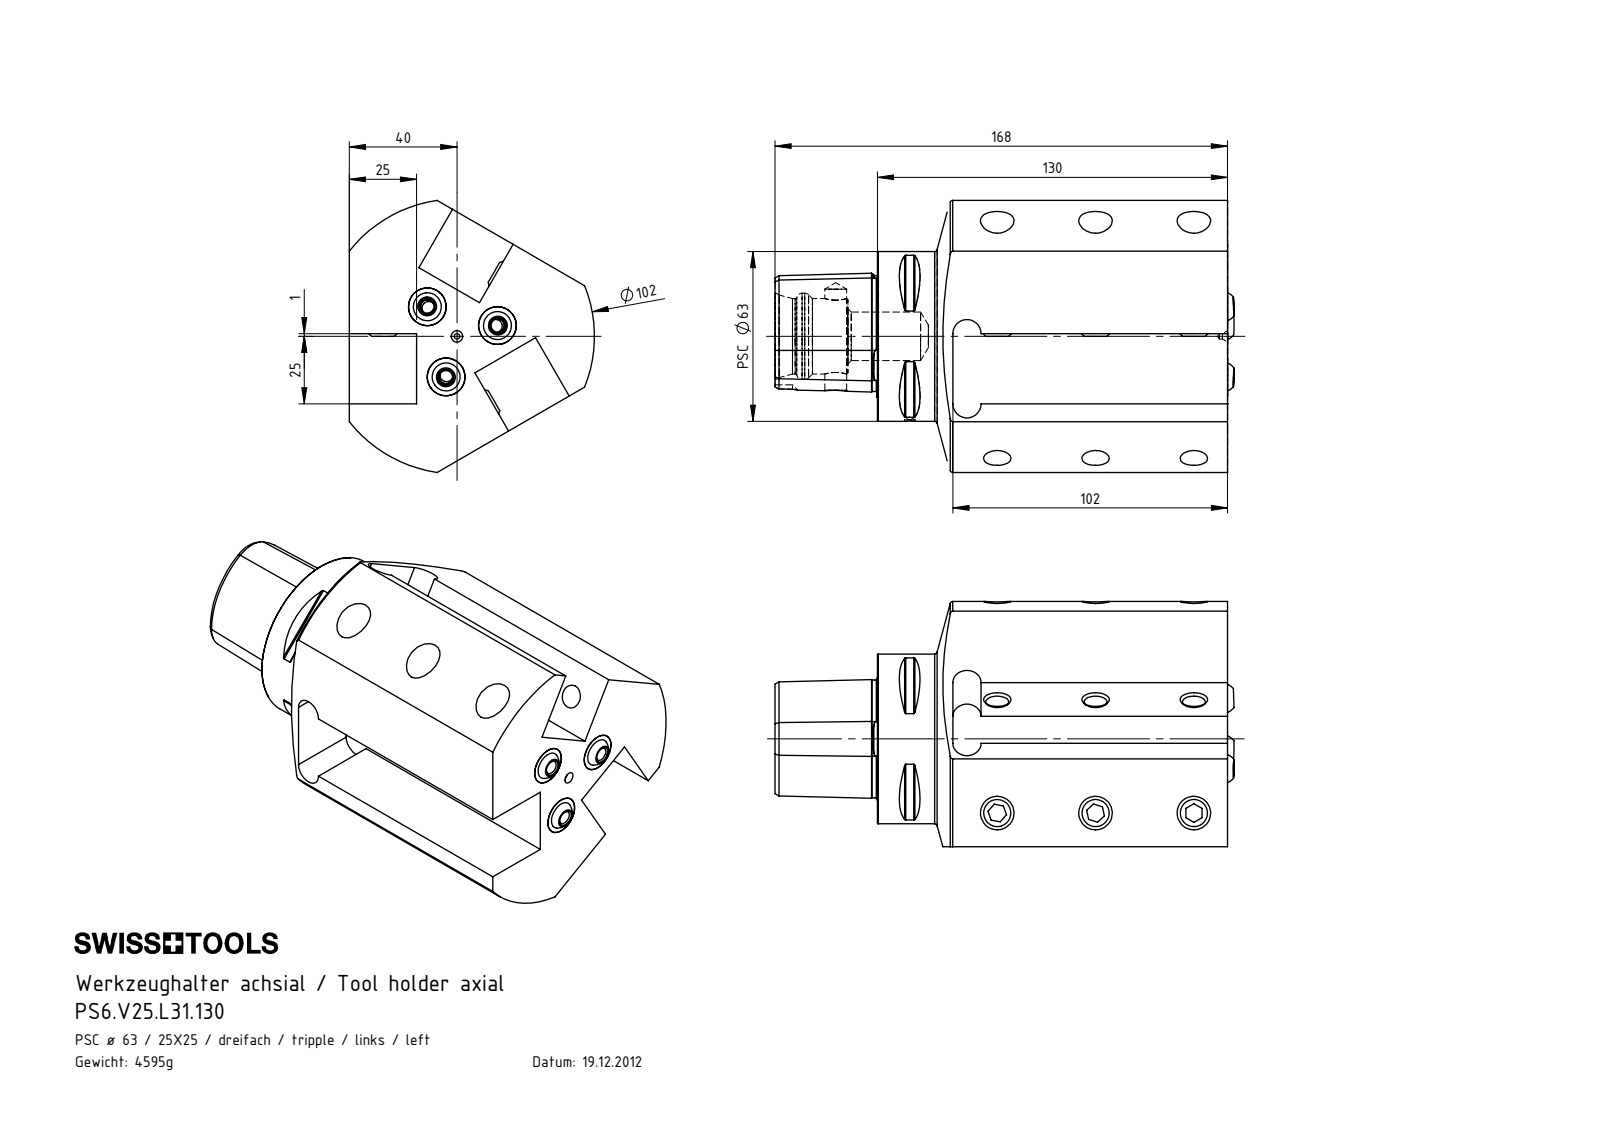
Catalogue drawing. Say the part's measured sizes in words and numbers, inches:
The part is named "KU1-U14.001.012_2; PS6.V25.L31.130; KU1-U14.001.012_1; KU1-U14.001.012 (+2 more)". Its 3-D file was written by "SolidWorks 2017 (CONFIG_CONTROL_DESIGN)". It is 16 solids with 415 faces: 127 planar, 124 cylindrical and 164 other. Overall it measures 6.709 by 3.973 by 3.583 inches. Its volume is 35.35 cubic inches and its surface area 163.6 square inches. Round holes: 9 of diameter 0.402, 9 of diameter 0.512, 6 of diameter 0.197, 3 of diameter 0.394, 3 of diameter 0.551, 1 of diameter 0.079, 1 of diameter 0.157, 1 of diameter 0.319, 1 of diameter 0.331, 1 of diameter 0.709, 1 of diameter 1.102, 1 of diameter 1.26. Round bosses or shafts: 9 of diameter 0.472, 1 of diameter 2.48. Partial cylindrical surfaces (rounded edges, fillets, slot ends): 8 of radius 0.02, 6 of radius 0.207, 1 of radius 0.236, 1 of radius 2.008. The main face-to-face distances are 0.984, 1.024, 4.016, 1.102, 5.118, 4.724, 3.622, 0.394, 0.236, 0.433. The hole center spacings are 1.437, 0.613, 1.061, 2.874, 1.083, 1.676, 2.598, 2.924.
